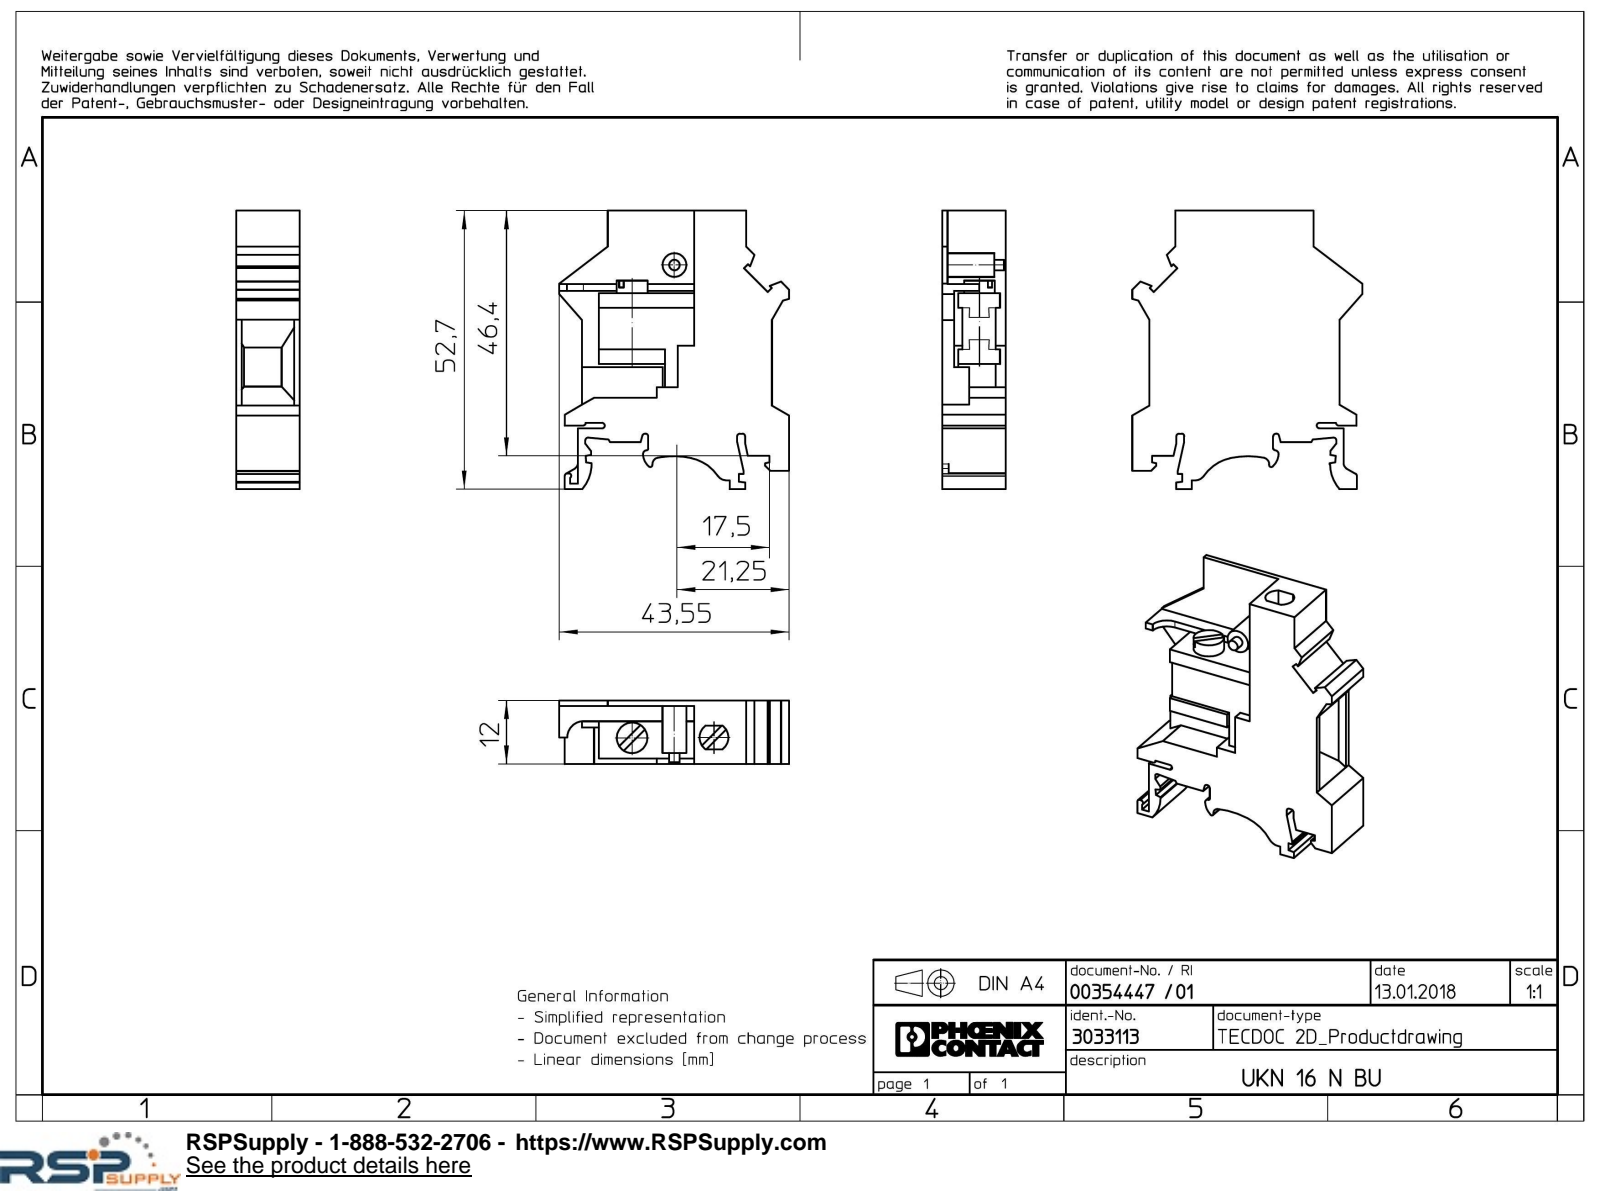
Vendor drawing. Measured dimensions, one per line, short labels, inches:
name: UKN_16_N_BU-select
written by: Creo Elements/Direct Modeling 18.1I 14-Aug-2016 (C) Parametric Technology GmbH (AUTOMOTIVE_DESIGN)
unit: in
bodies: 1 solid, 161 faces (132 planar, 29 cylindrical, 0 other)
size: 2.075 × 1.715 × 0.472
volume: 0.844 in³; area: 12.46 in²
bosses: 1× ⌀0.228, 1× ⌀0.177, 1× ⌀0.079
rounds: 8× R0.02, 1× R0.012, 1× R0.016, 1× R0.02, 1× R0.021, 1× R0.028, 1× R0.039, 1× R0.047
face distances: 0.472, 0.433, 0.049, 0.039, 0.384, 0.089, 0.311, 0.28, 0.031, 0.709
